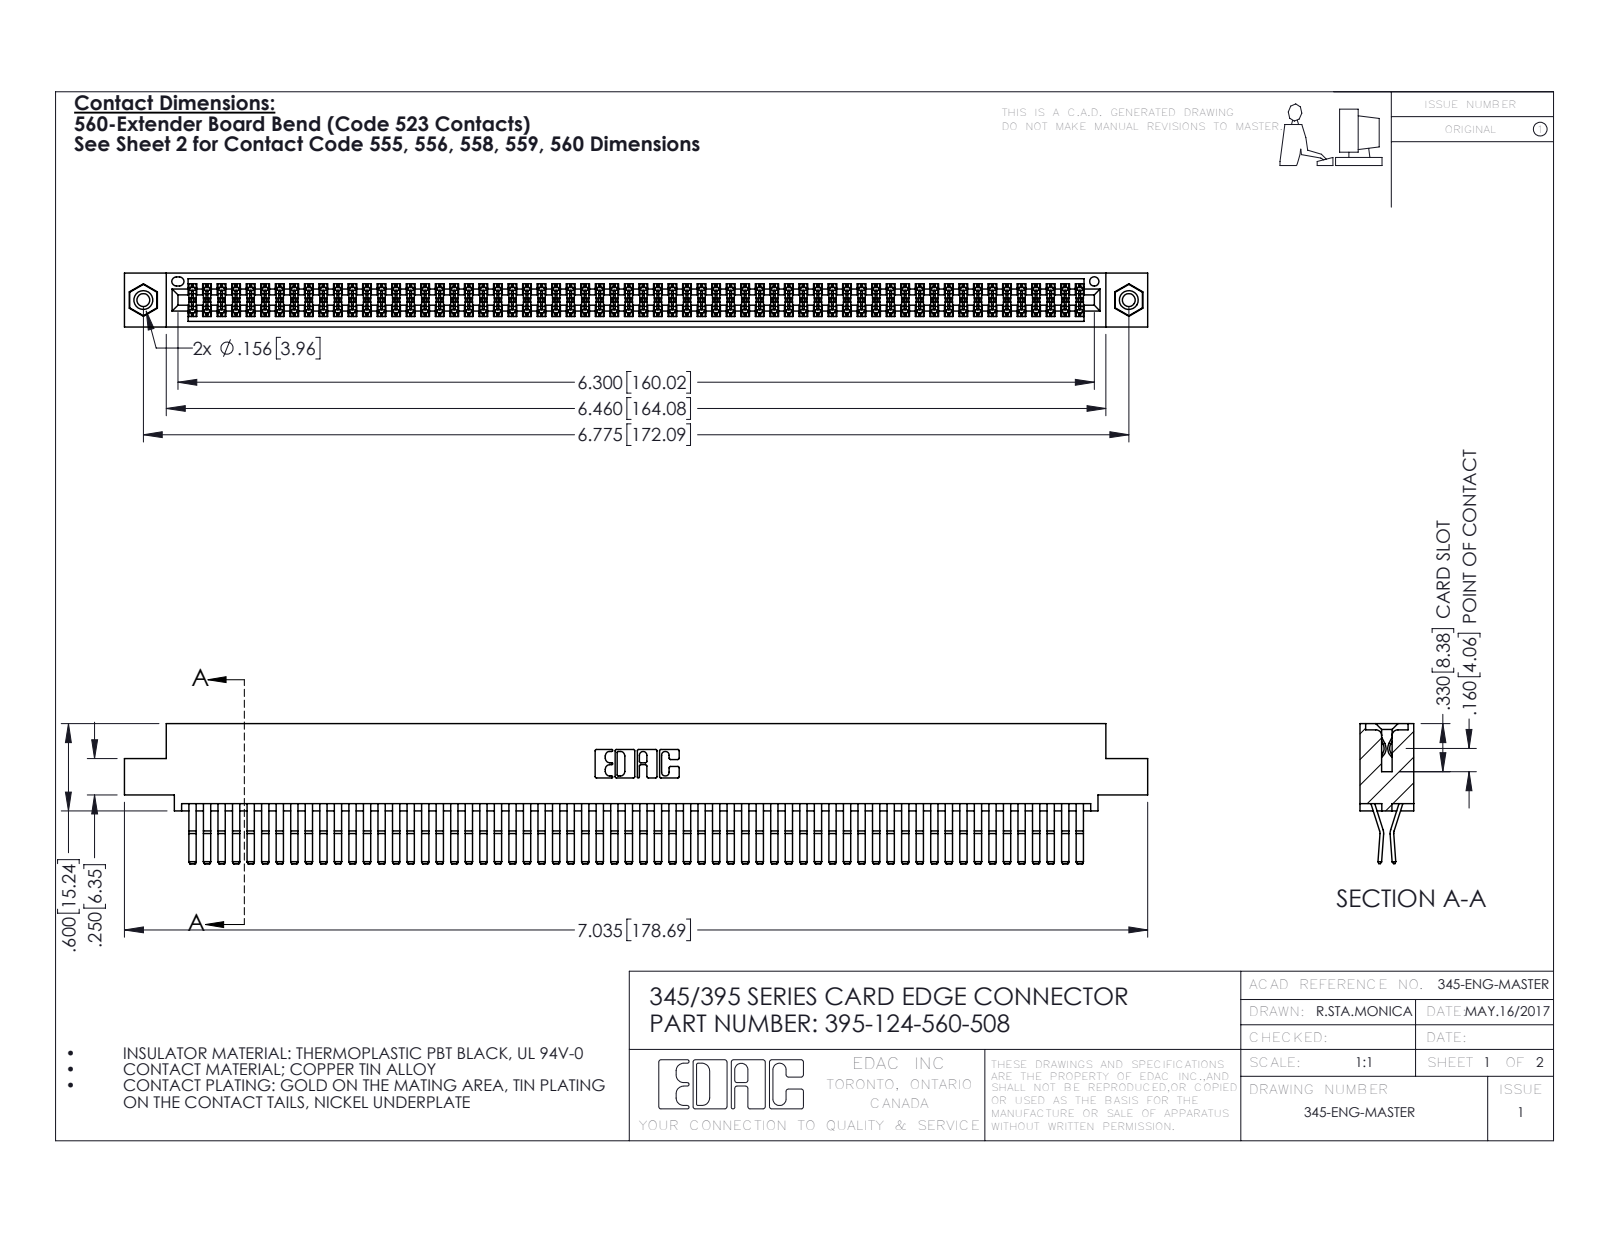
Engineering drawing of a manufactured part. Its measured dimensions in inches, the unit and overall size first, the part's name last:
Units: inches
Overall size (bounding box): 7.035 × 0.962 × 0.37
Round holes (diameter × count): ⌀0.089 ×2, ⌀0.125 ×2, ⌀0.156 ×2, ⌀0.064 ×1
Round bosses / shafts (diameter × count): ⌀0.155 ×2
Partial cylindrical surfaces — rounded edges, fillets, slot ends (radius × count): R0.006 ×187, R0.01 ×22, R0.007 ×6, R0.031 ×6, R0.026 ×3, R0.01 ×2, R0.014 ×2, R0.019 ×2
Main face-to-face distances: 0.025, 0.072, 0.298, 0.37, 0.2, 0.098, 0.272, 0.225, 0.175, 0.149
Hole centre spacings: 0.27, 6.539, 6.775
Volume: 1.115 in³ · Surface area: 45.88 in²
Bodies: 127 solids, 6638 faces (4208 planar, 2414 cylindrical, 16 other)
Part name (STEP PRODUCT): 345-292-001_560 Tail; 345-250-001_345-250-003-102; 395-124-560-508; 345 Part_0.110 Offset - 0.156 Dia-TI
STEP written by: SolidWorks 2016 (CONFIG_CONTROL_DESIGN)
